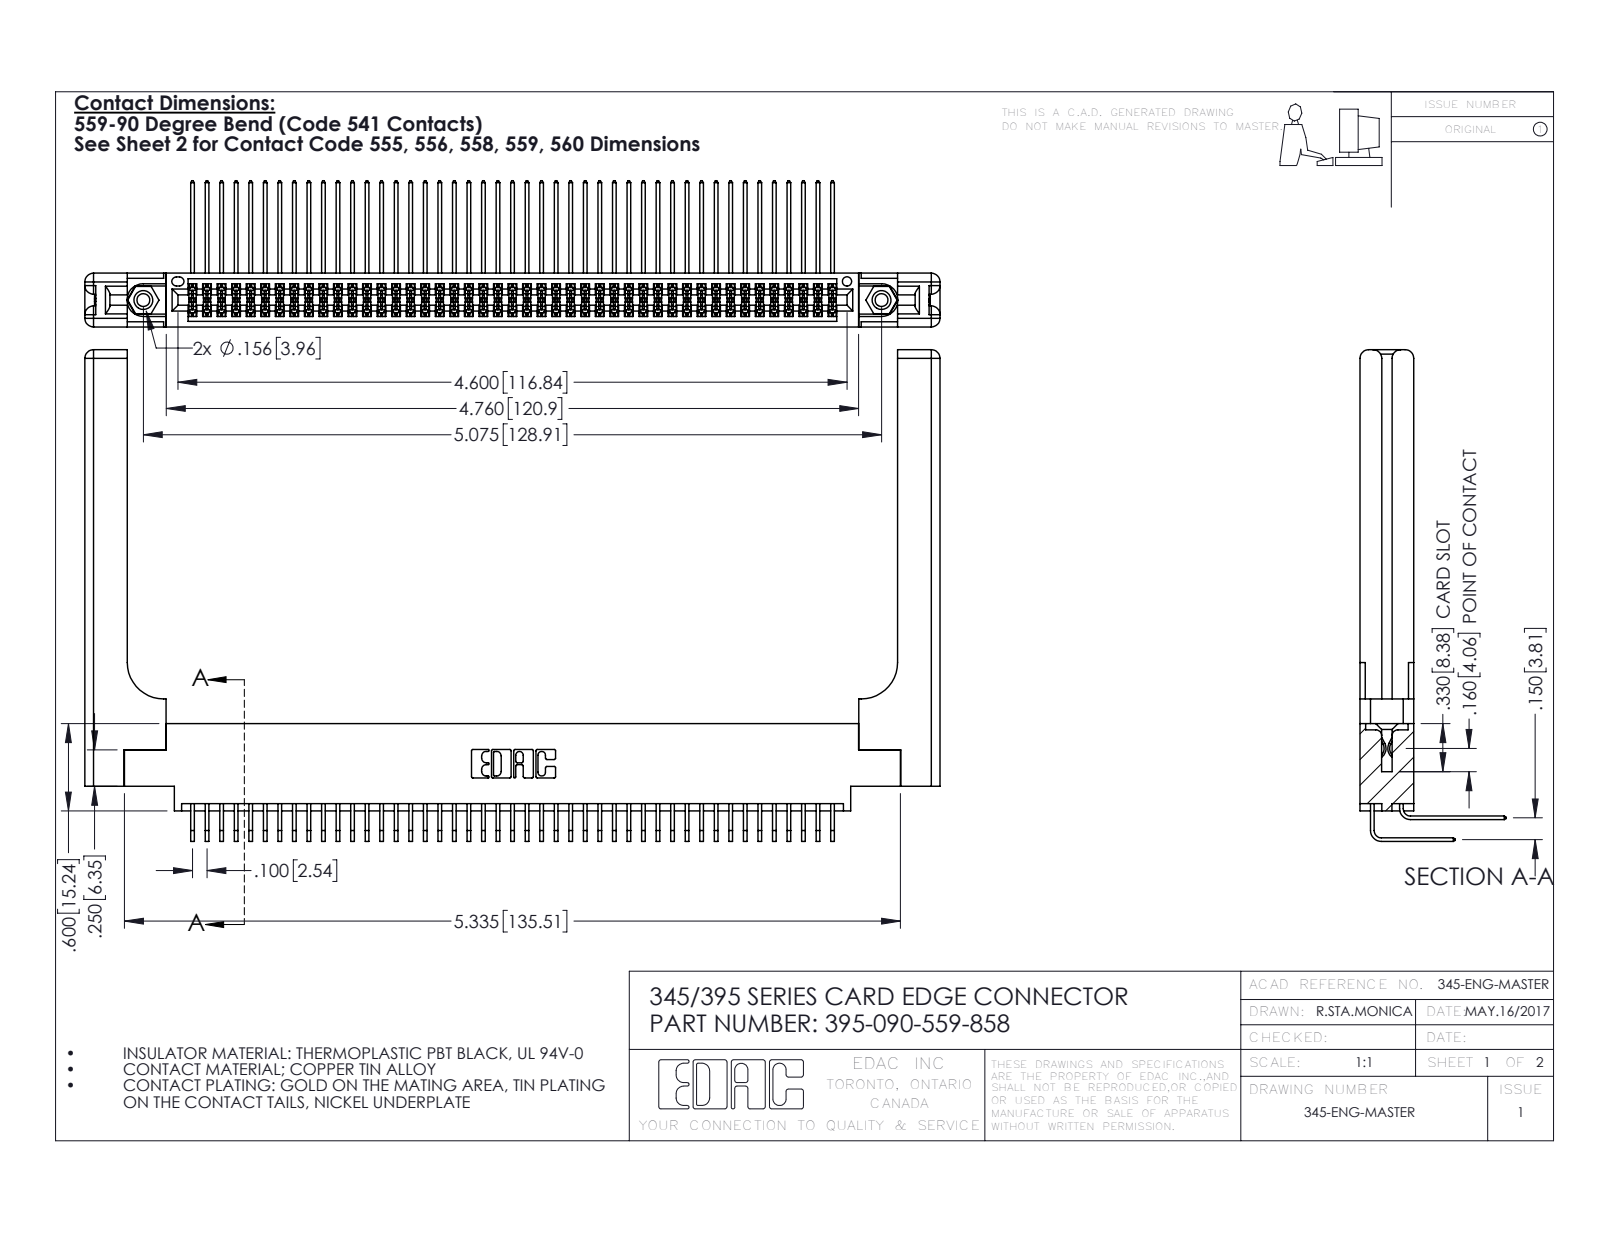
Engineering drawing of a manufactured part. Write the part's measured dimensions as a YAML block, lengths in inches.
part_name: "395-090-559-858; 345-292-001_558 559 Tail - 1; 345-250-001_345-250-001-102; 345-292-001_559 Tail - 2 (+2 more)"
step_written_by: "SolidWorks 2016 (CONFIG_CONTROL_DESIGN)"
units: inches
bodies: {solids: 95, faces: 5066, planar: 3382, cylindrical: 1624, other: 60}
overall_size: [5.879, 3.379, 1.005]
volume: 1.429
surface_area: 46.17
round_holes:
  - {diameter: 0.089, count: 2}
  - {diameter: 0.125, count: 2}
  - {diameter: 0.156, count: 2}
  - {diameter: 0.064, count: 1}
round_bosses_or_shafts:
  - {diameter: 0.155, count: 2}
partial_cylinders:
  - {radius: 0.006, count: 135}
  - {radius: 0.01, count: 22}
  - {radius: 0.06, count: 16}
  - {radius: 0.007, count: 6}
  - {radius: 0.031, count: 6}
  - {radius: 0.026, count: 3}
  - {radius: 0.014, count: 2}
  - {radius: 0.019, count: 2}
face_to_face_distances: [0.072, 0.37, 0.298, 0.098, 0.272, 0.025, 0.2, 0.225, 0.15, 0.175]
hole_center_spacings: [0.27, 4.839, 5.075]
